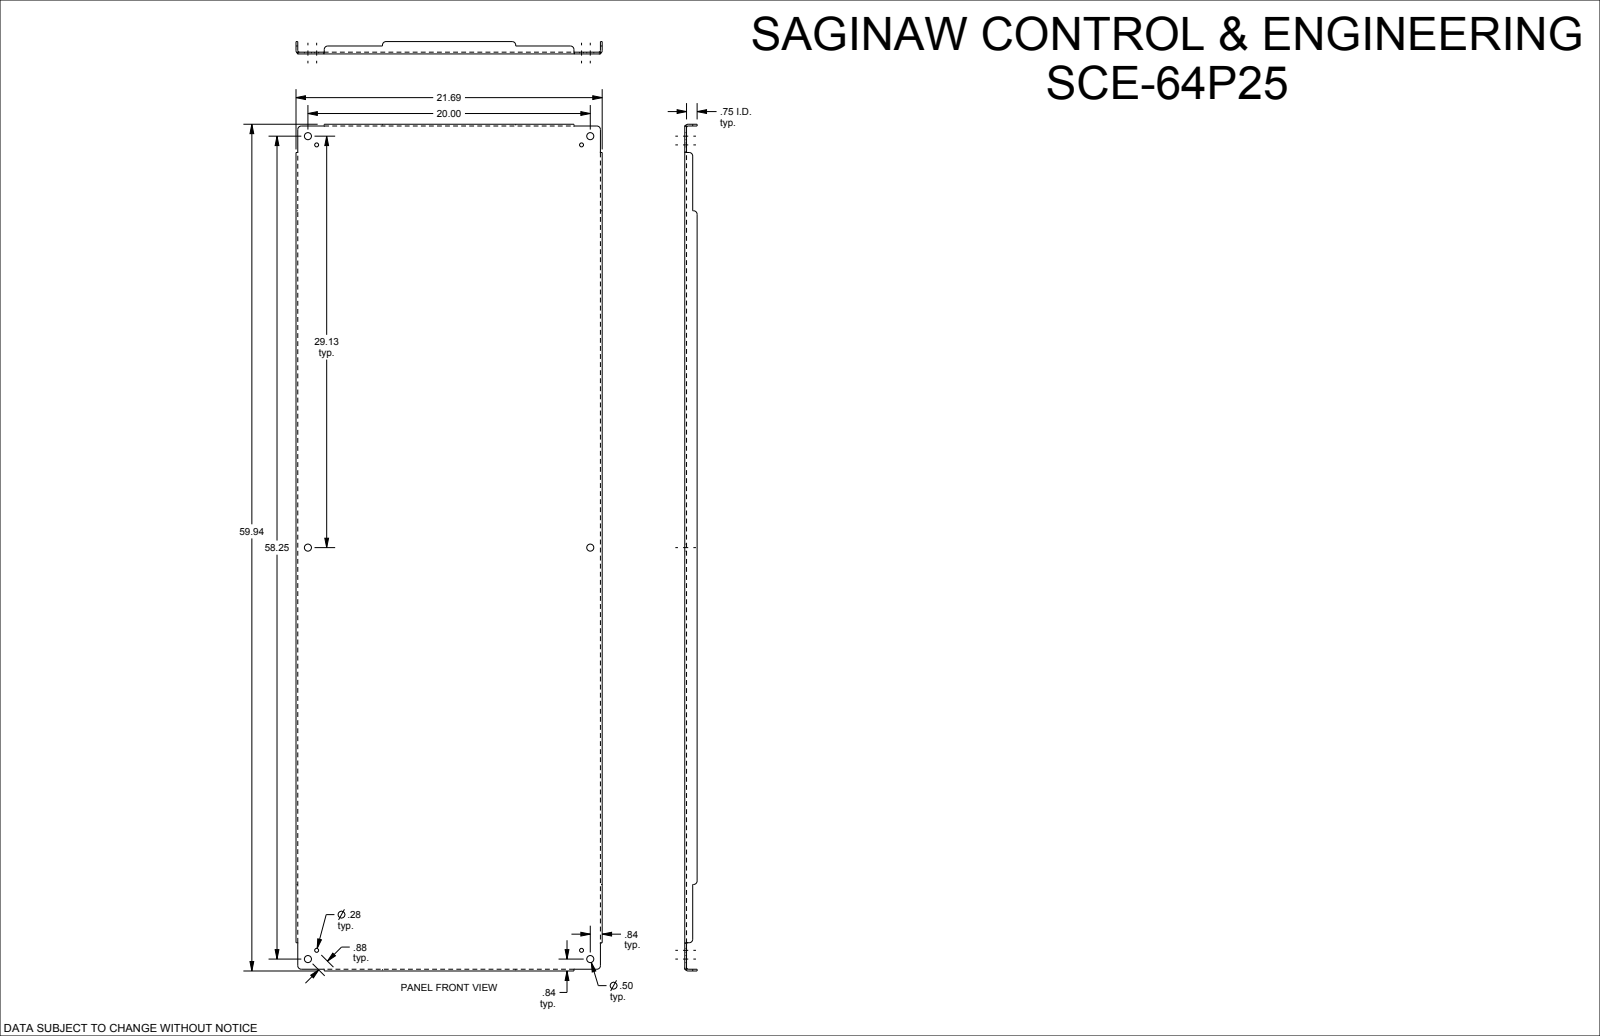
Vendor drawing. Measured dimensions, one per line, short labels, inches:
name: SCE-64P25
written by: SolidWorks 2019 (CONFIG_CONTROL_DESIGN)
unit: in
bodies: 1 solid, 108 faces (46 planar, 38 cylindrical, 24 other)
size: 59.938 × 21.688 × 0.875
volume: 173.2 in³; area: 2 793 in²
holes: 6× ⌀0.5, 4× ⌀0.281
rounds: 12× R0.25, 4× R0.112, 4× R0.237
face distances: 0.125, 21.563, 21.438, 21.687, 0.125, 59.813, 0.75, 0.875, 59.687, 59.938
hole spacings: 0.875, 19.391, 28.513, 29.125, 34.471, 35.331, 57.634, 60.803
